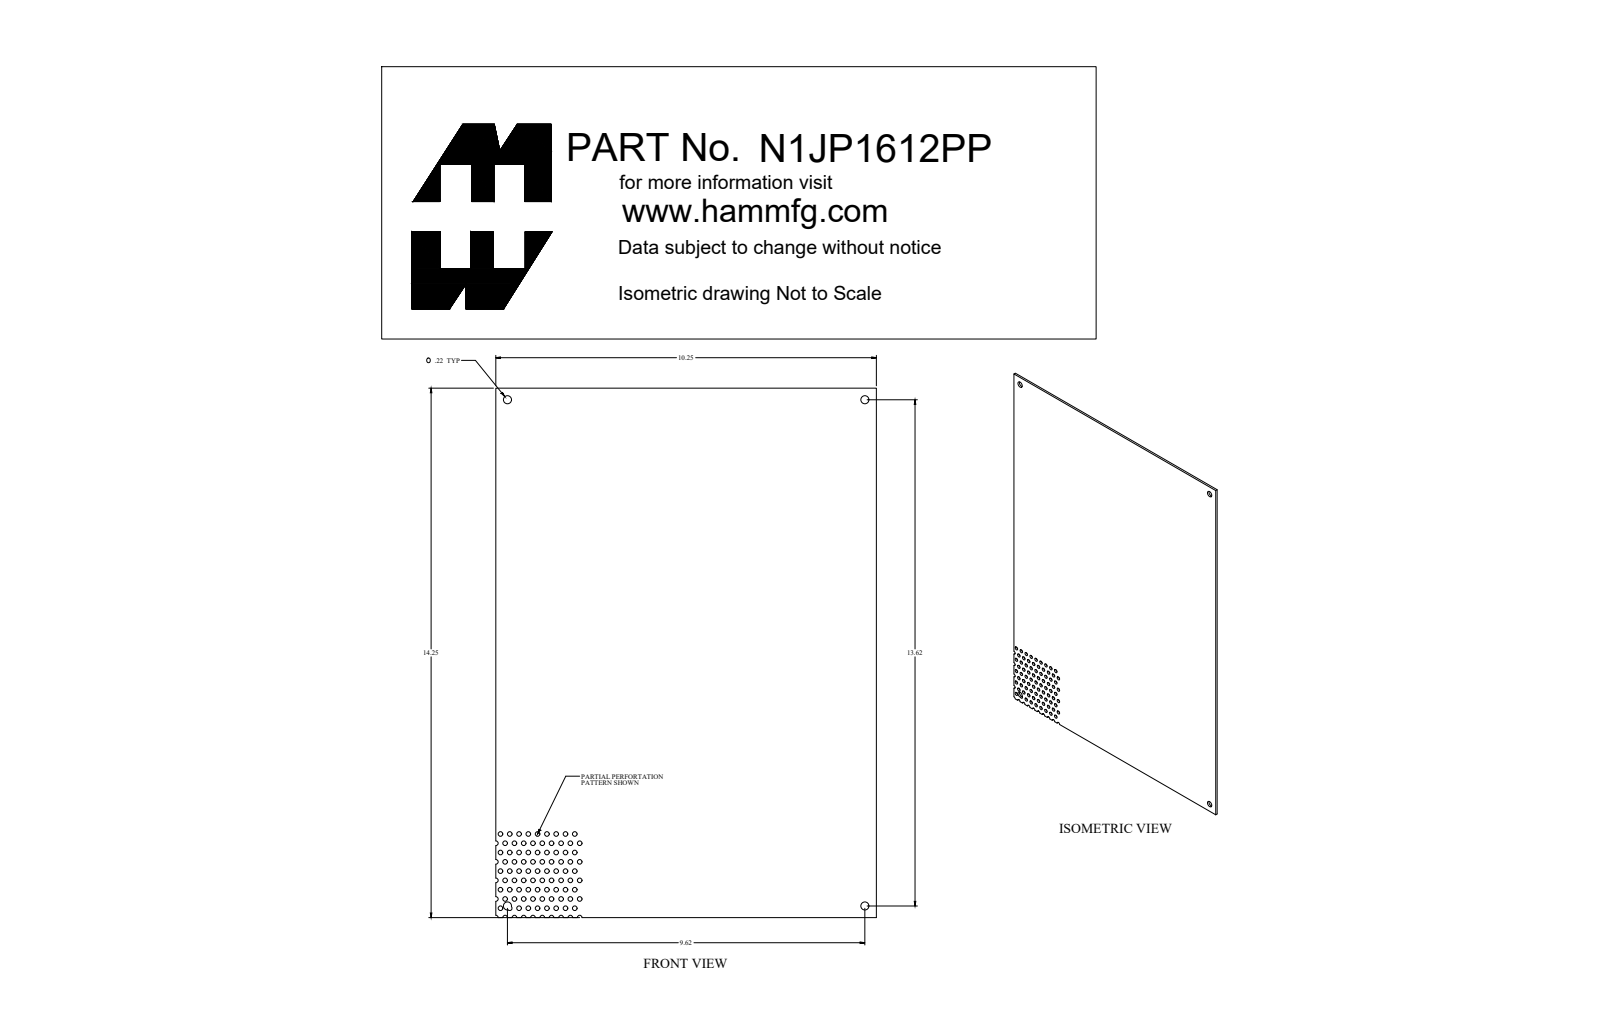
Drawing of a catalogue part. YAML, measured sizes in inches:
part_name: "N1JP1612PP"
step_written_by: "SolidWorks 2018 (AUTOMOTIVE_DESIGN)"
units: inches
bodies: {solids: 1, faces: 203, planar: 19, cylindrical: 184, other: 0}
overall_size: [14.25, 10.25, 0.072]
volume: 10.43
surface_area: 295.7
round_holes:
  - {diameter: 0.125, count: 75}
  - {diameter: 0.125, count: 5}
  - {diameter: 0.218, count: 4}
partial_cylinders:
  - {radius: 0.063, count: 10}
  - {radius: 0.062, count: 5}
face_to_face_distances: [0.072, 10.25, 14.25]
hole_center_spacings: [0.25, 0.5, 0.559, 0.707, 0.75, 0.28, 0.45, 0.673]
